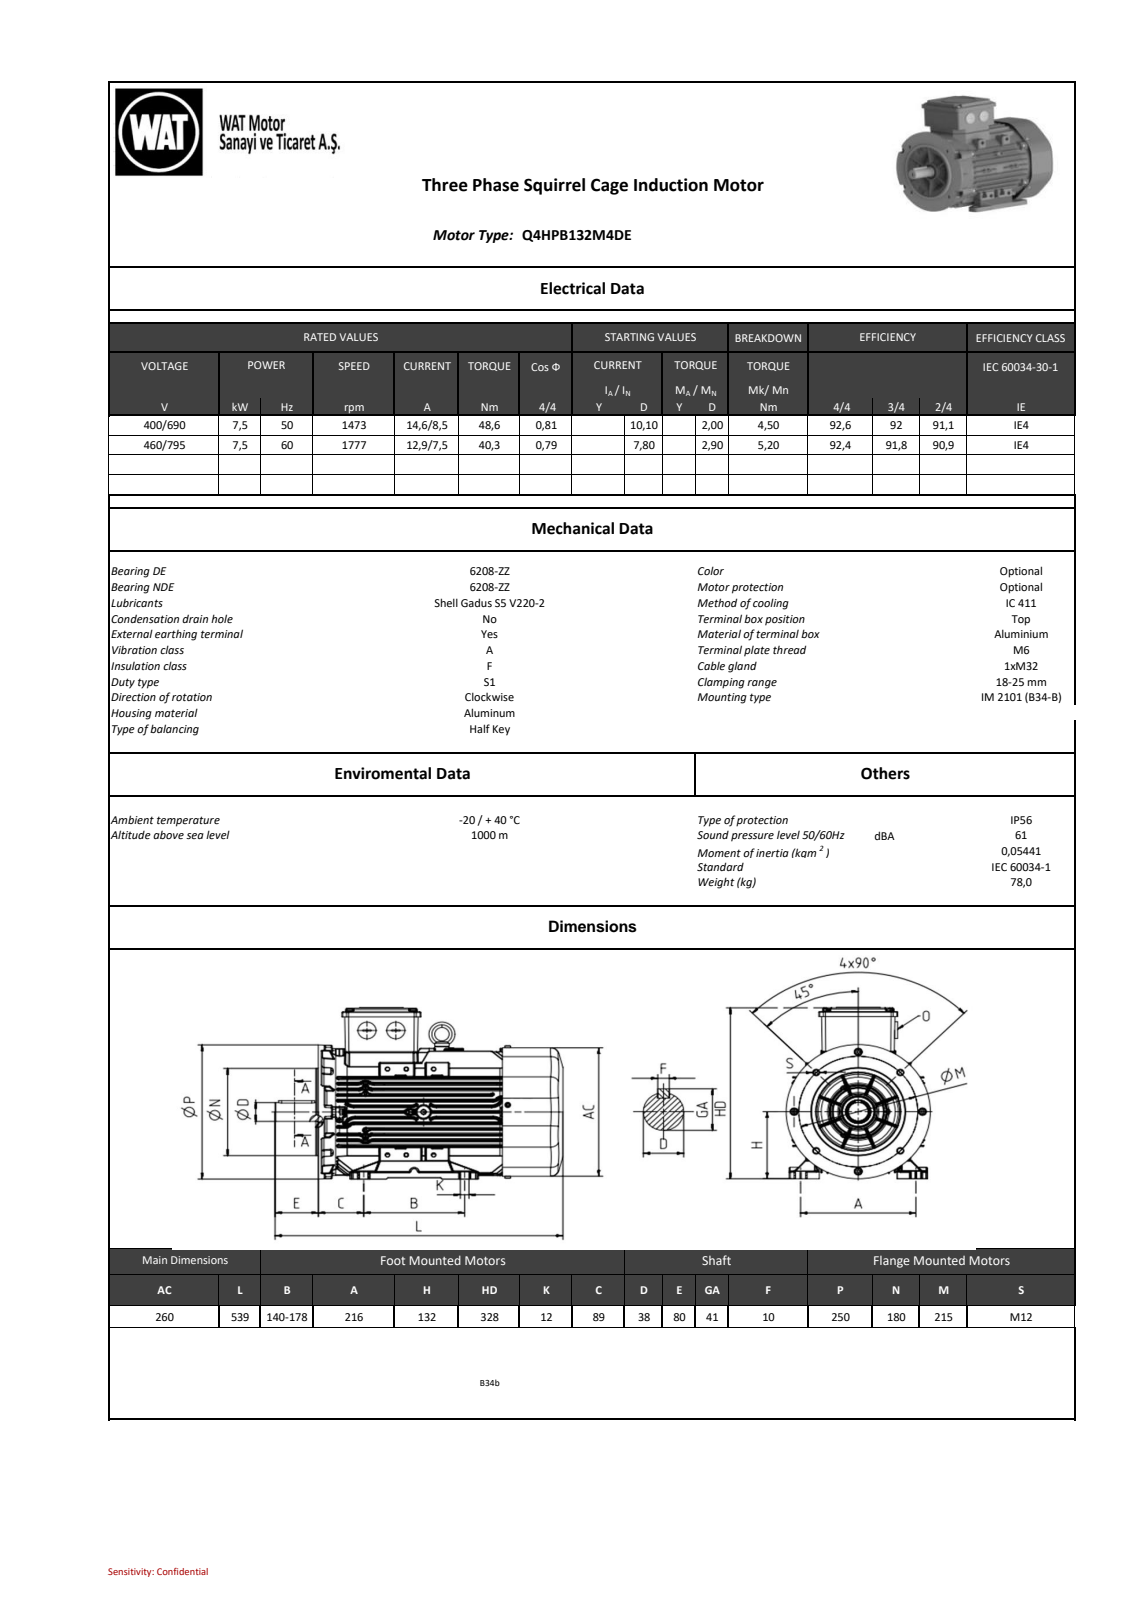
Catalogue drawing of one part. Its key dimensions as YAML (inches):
part_name: "26000438DCC3wigl"
step_written_by: "SIEMENS PLM Software NX 11.0 (AUTOMOTIVE_DESIGN)"
units: inches
bodies: {solids: 0, faces: 15909, planar: 3339, cylindrical: 5062, other: 7508}
overall_size: [21.219, 12.686, 10.541]
round_holes:
  - {diameter: 0.217, count: 8}
  - {diameter: 0.157, count: 6}
  - {diameter: 0.262, count: 4}
  - {diameter: 0.335, count: 4}
  - {diameter: 0.165, count: 2}
  - {diameter: 0.316, count: 2}
  - {diameter: 0.333, count: 2}
  - {diameter: 0.334, count: 2}
  - {diameter: 0.591, count: 2}
  - {diameter: 1.102, count: 2}
  - {diameter: 1.197, count: 2}
  - {diameter: 0.22, count: 1}
round_bosses_or_shafts:
  - {diameter: 0.315, count: 11}
  - {diameter: 0.165, count: 5}
  - {diameter: 0.886, count: 4}
  - {diameter: 0.512, count: 4}
  - {diameter: 1.496, count: 3}
  - {diameter: 1.26, count: 2}
  - {diameter: 0.335, count: 2}
  - {diameter: 9.075, count: 1}
partial_cylinders:
  - {radius: 0.031, count: 1497}
  - {radius: 0.039, count: 1376}
  - {radius: 0.02, count: 154}
  - {radius: 0.004, count: 122}
  - {radius: 0.079, count: 110}
  - {radius: 0.059, count: 41}
  - {radius: 0.118, count: 38}
  - {radius: 0.008, count: 21}
face_to_face_distances: [0.41, 0.059, 0.416, 0.118, 0.405, 0.82, 4.944, 4.535, 4.13, 3.719]
hole_center_spacings: [3.835, 6.711, 2.45, 3.465, 0.501, 2.951, 4.173, 4.744]
